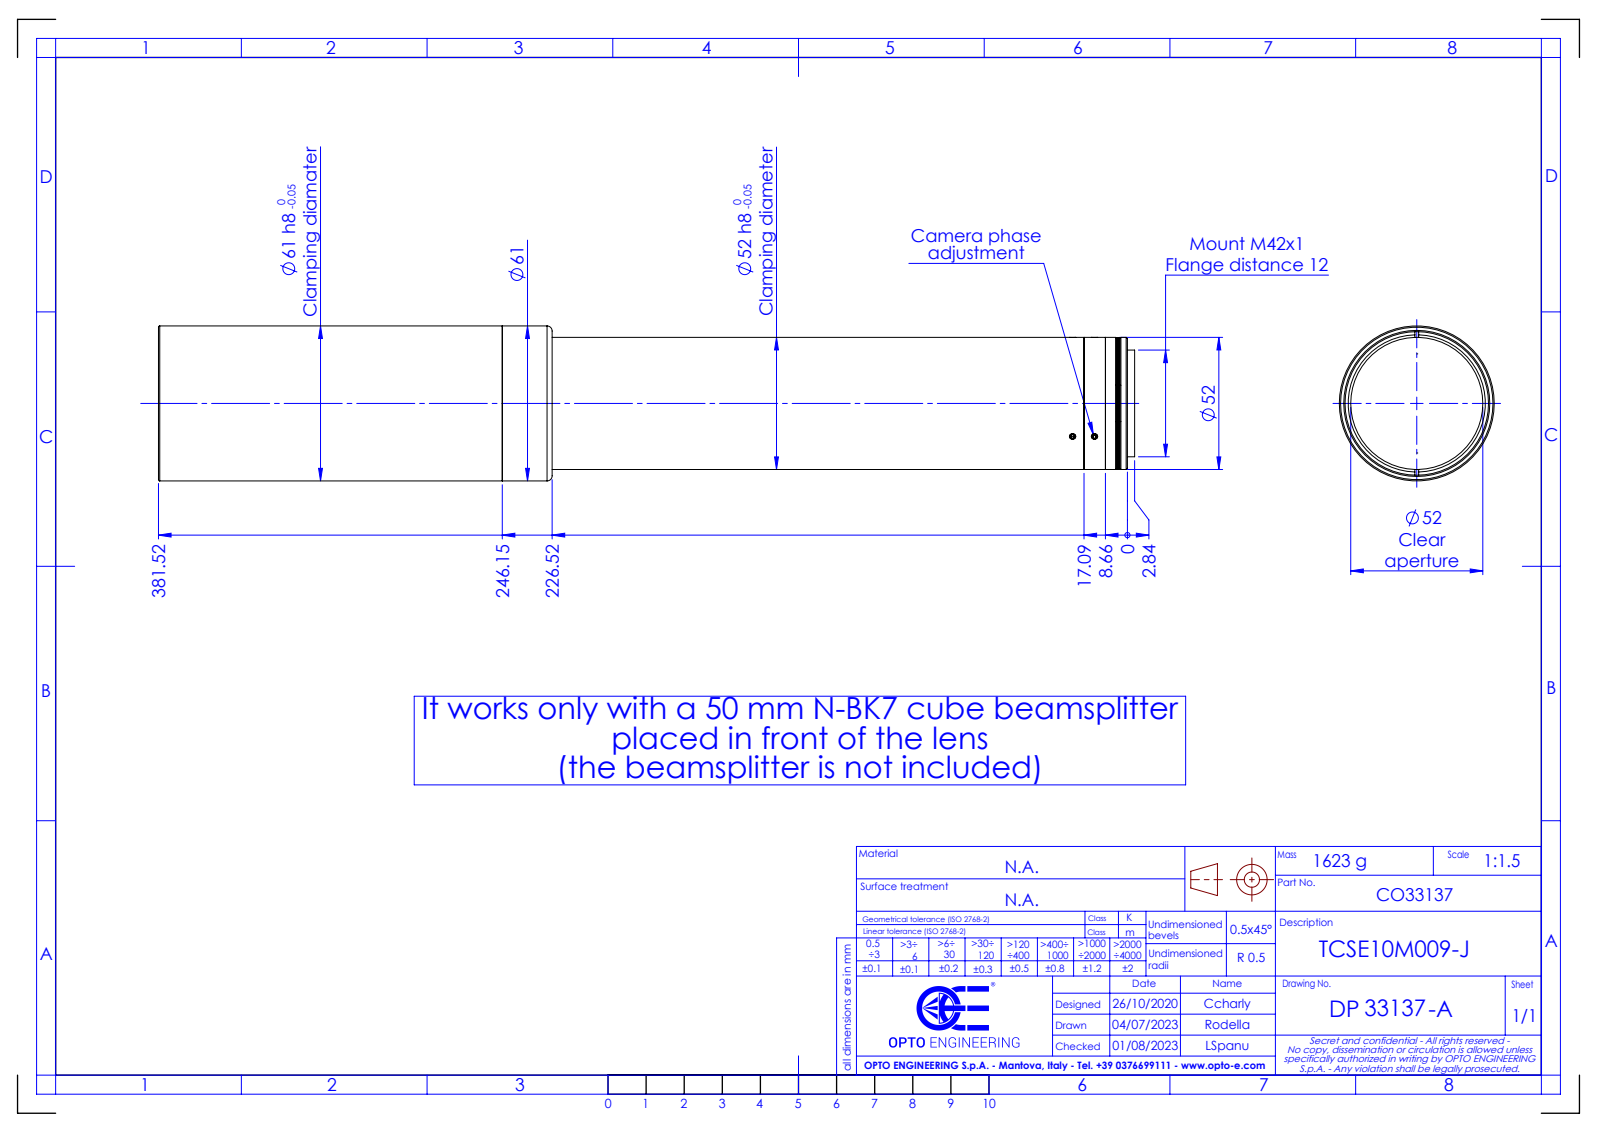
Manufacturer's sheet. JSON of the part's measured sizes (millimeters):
{"part_name": "DP33137-A_TCSE10M009-J", "step_written_by": "SolidWorks 2021 (CONFIG_CONTROL_DESIGN)", "units": "millimeters", "bodies": {"solids": 0, "faces": 116, "planar": 53, "cylindrical": 38, "other": 25}, "overall_size": [384.36, 61, 61], "round_holes": [[2.5, 1], [37.5, 1], [38, 1], [53, 1], [56.5, 1]], "round_bosses_or_shafts": [[61, 1], [52, 1], [51.8, 1], [42, 1]], "face_to_face_distances": [2.1, 2.56, 4.66, 246.15, 243.59, 241.49, 17.09, 14.53, 12.43, 229.06]}
